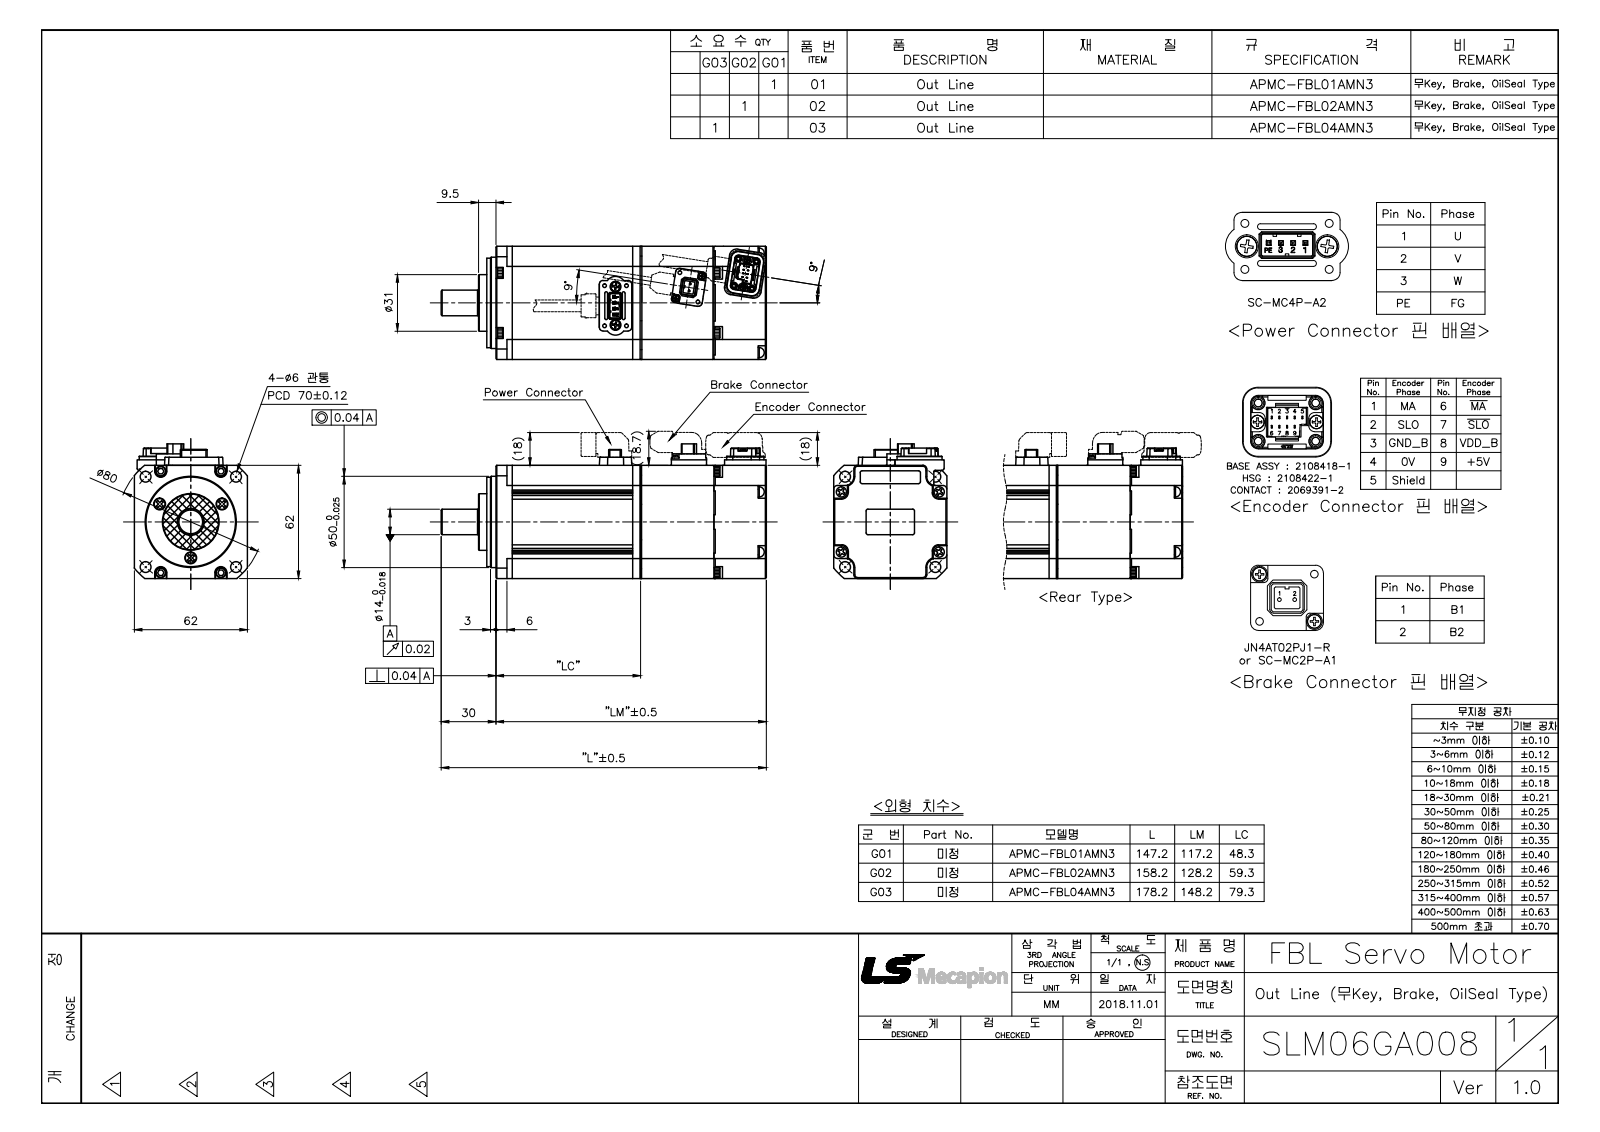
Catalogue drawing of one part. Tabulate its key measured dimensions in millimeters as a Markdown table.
| quantity | value |
| --- | --- |
| part name | SLM06GA004G02_Out Line(APMC-FBL02AMN2) |
| STEP written by | SolidWorks 2011 (AUTOMOTIVE_DESIGN) |
| units | millimeters |
| bodies | 50 solids, 2073 faces (1276 planar, 578 cylindrical, 219 other) |
| overall size | 158.2 × 73.8 × 62 |
| volume | 448 719 mm³ |
| surface area | 98 083 mm² |
| round holes (diameter × count) | 2.1 × 10, 3 × 10, 3.5 × 8, 2 × 6, 6 × 6, 3.1 × 4, 1 × 2, 3.3 × 1, 3.4 × 1, 13 × 1, 15.3 × 1 |
| round bosses / shafts (diameter × count) | 5.4 × 6, 5.6 × 4, 5.5 × 4, 4.2 × 2, 3.6 × 2, 3.5 × 2, 2.2 × 2, 0.9 × 2 |
| partial cylindrical surfaces (radius × count) | 0.2 × 20, 0.3 × 20, 1 × 14, 2 × 12, 0.15 × 9, 3 × 8, 0.45 × 7, 0.11 × 6 |
| main face-to-face distances | 62, 4.3, 0.5, 0.7, 46, 50.3, 44.5, 40.2, 90.5, 40.9 |
| hole center spacings | 6.02, 8.5, 8.8, 9.43, 15.29, 16.01, 22.32, 31.47 |
